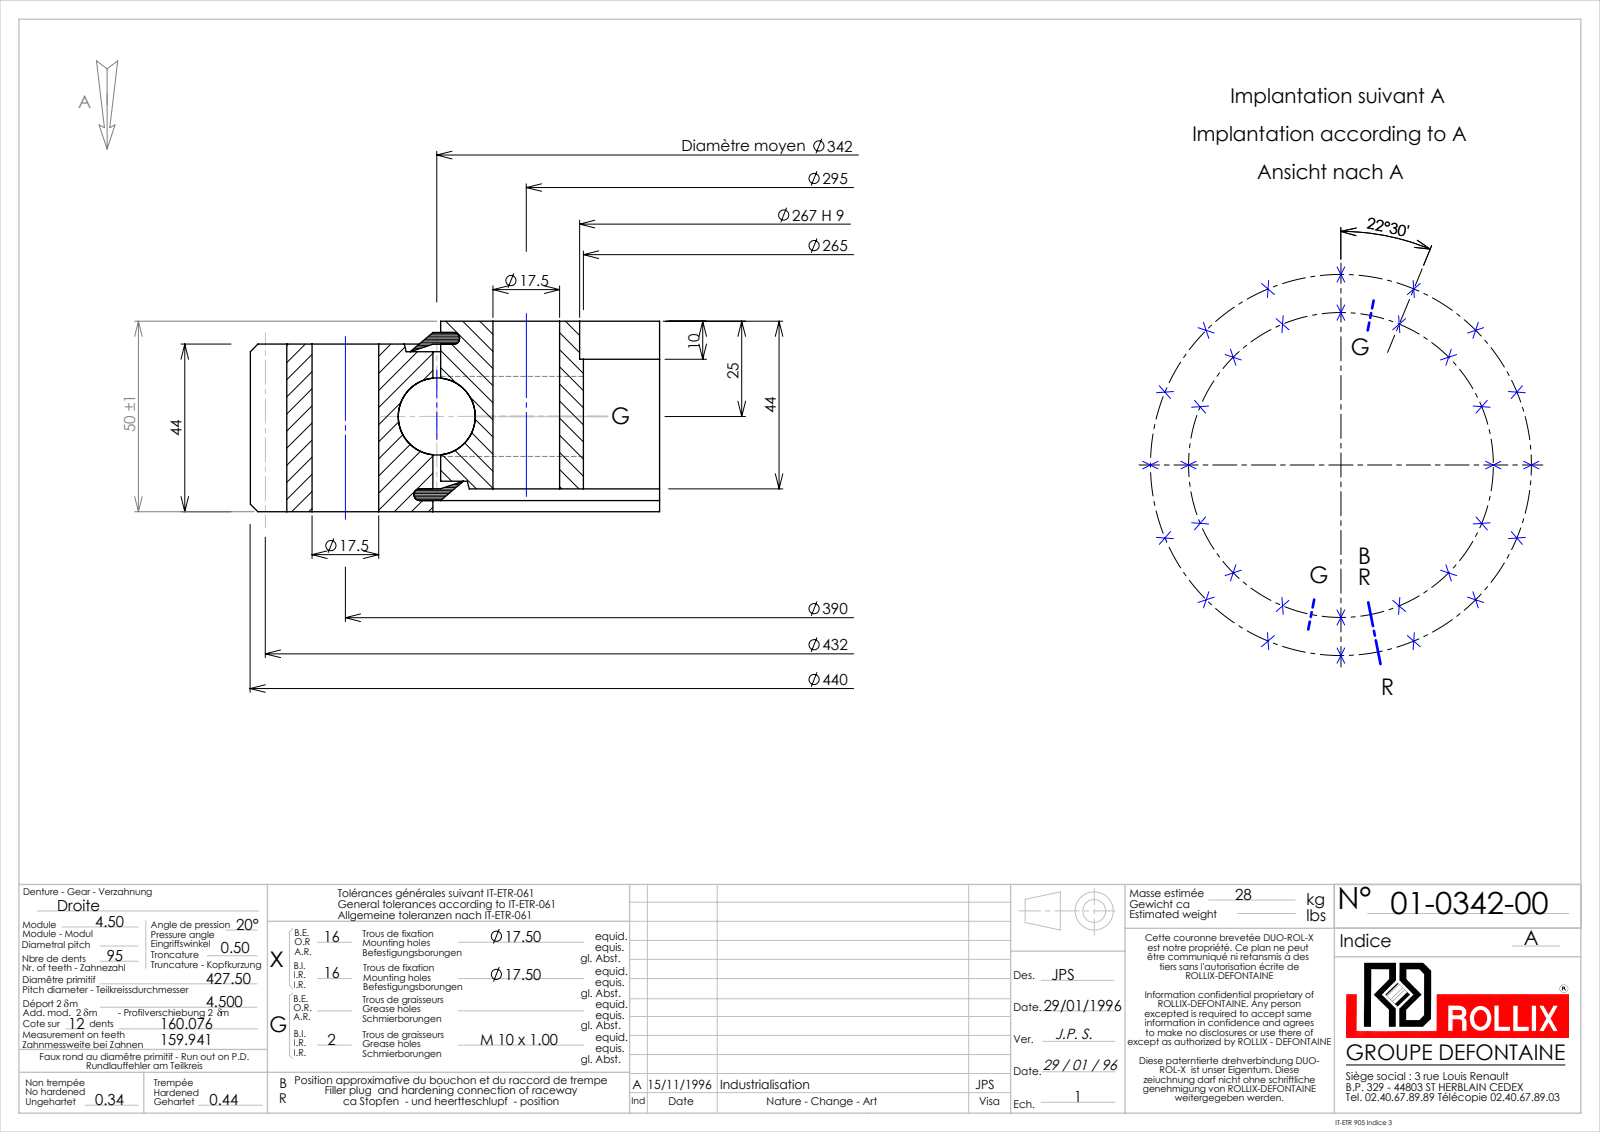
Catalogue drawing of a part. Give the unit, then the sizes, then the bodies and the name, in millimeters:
Units: millimetres
Overall size (bounding box): 439.99 × 439.94 × 50
Round holes (diameter × count): ⌀17.5 ×32, ⌀9 ×2, ⌀265 ×1, ⌀267 ×1, ⌀344.03 ×1
Round bosses / shafts (diameter × count): ⌀339.98 ×1
Partial cylindrical surfaces — rounded edges, fillets, slot ends (radius × count): R210.38 ×1, R220 ×1
Main face-to-face distances: 44, 6, 50, 38, 2.95, 6.05, 43.95, 47.05, 3.05, 41.05
Hole centre spacings: 138.22, 286, 336.05, 81.46, 316.95, 382.51, 194.34, 244.51
Volume: 3 256 000 mm³ · Surface area: 591 159 mm²
Bodies: 5 solids, 703 faces (205 planar, 275 cylindrical, 223 other)
Part name (STEP PRODUCT): 01-0342-00
STEP written by: SolidWorks 2016 (CONFIG_CONTROL_DESIGN)
